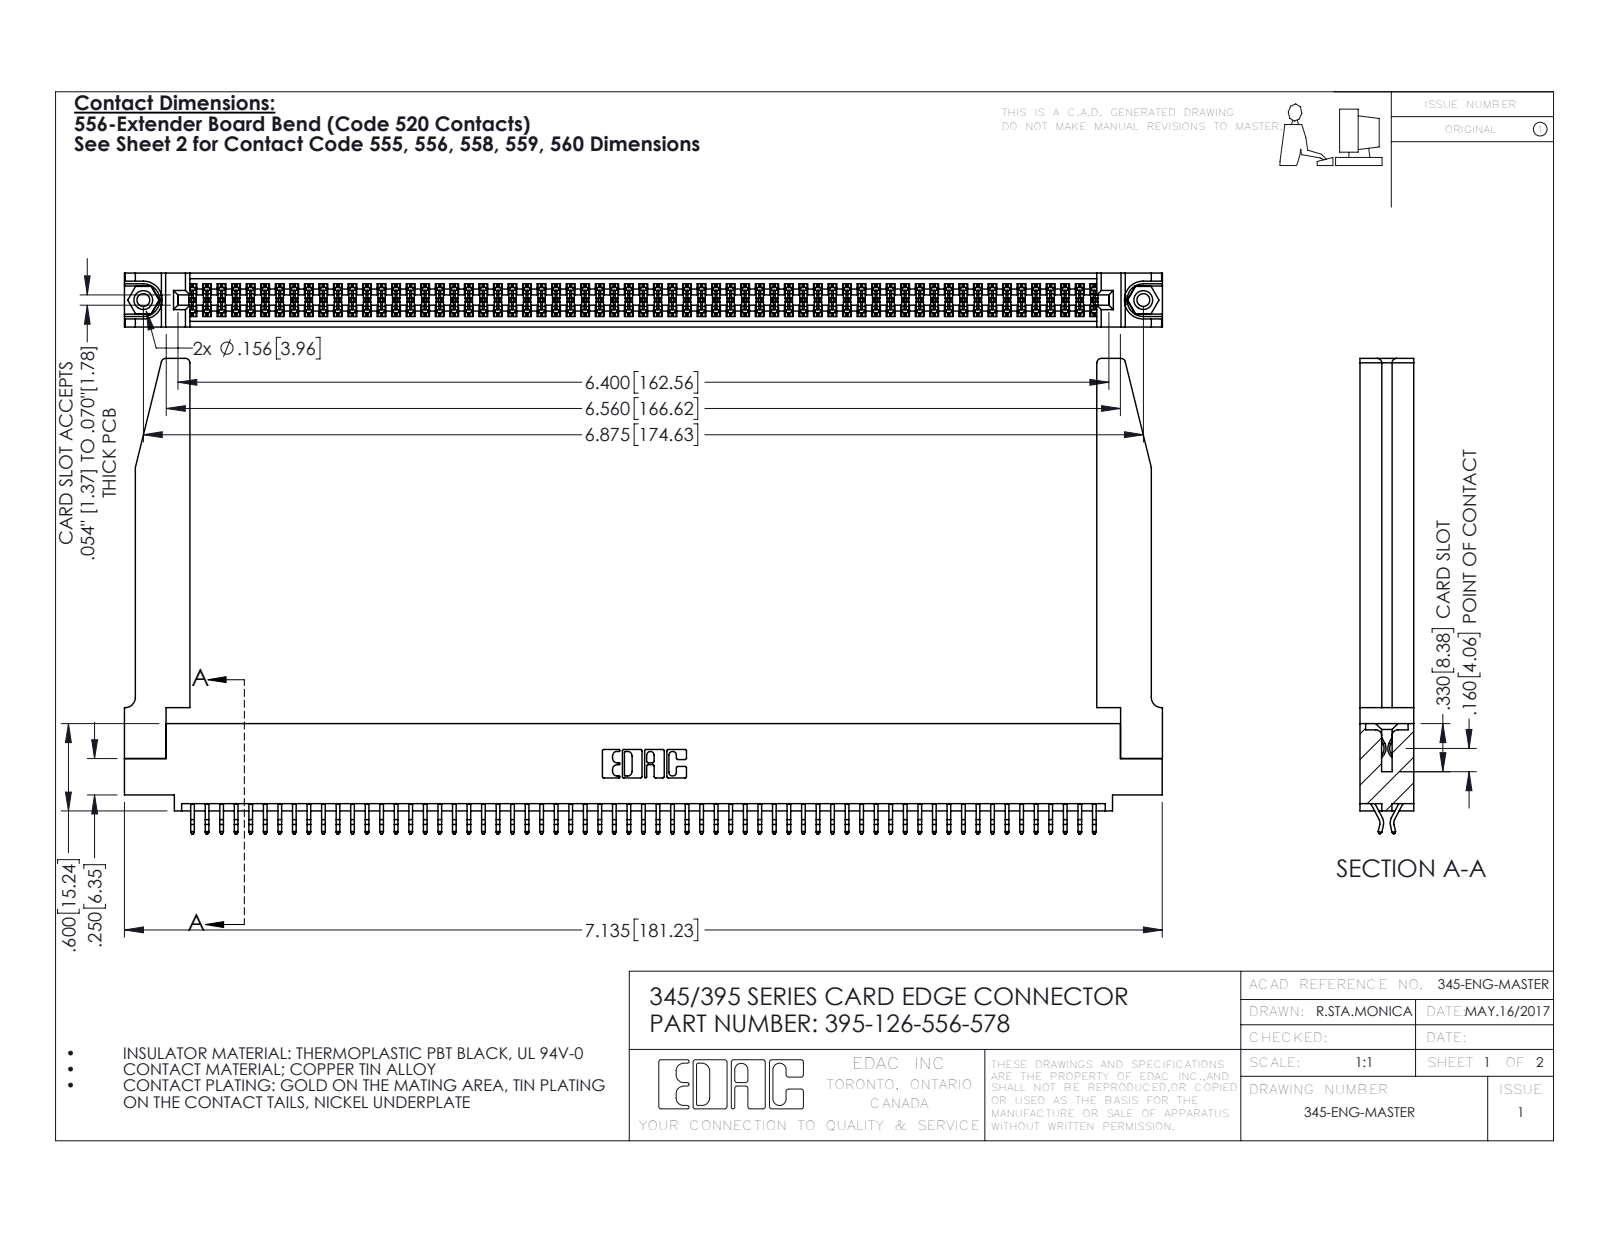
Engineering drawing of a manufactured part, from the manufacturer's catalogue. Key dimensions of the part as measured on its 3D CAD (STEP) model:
Part name (STEP PRODUCT): 345-250-001_345-250-001-102; 395-126-556-578; 345-220-078_345-220-078; 345 Part_0.110 Offset - 0.156 Dia-TH (+1 more)
STEP written by: SolidWorks 2016 (CONFIG_CONTROL_DESIGN)
Units: inches
Bodies: 131 solids, 7420 faces (4888 planar, 2480 cylindrical, 52 other)
Overall size (bounding box): 7.136 × 3.267 × 0.37
Volume: 1.556 in³ · Surface area: 51.81 in²
Round holes (diameter × count): ⌀0.089 ×2, ⌀0.125 ×2, ⌀0.156 ×2, ⌀0.064 ×1
Round bosses / shafts (diameter × count): ⌀0.155 ×2
Partial cylindrical surfaces — rounded edges, fillets, slot ends (radius × count): R0.006 ×189, R0.01 ×22, R0.03 ×8, R0.007 ×6, R0.031 ×6, R0.026 ×3, R0.01 ×2, R0.014 ×2
Main face-to-face distances: 0.072, 0.298, 0.37, 0.025, 0.2, 0.098, 0.272, 0.225, 0.175, 0.148
Hole centre spacings: 0.27, 6.639, 6.875
